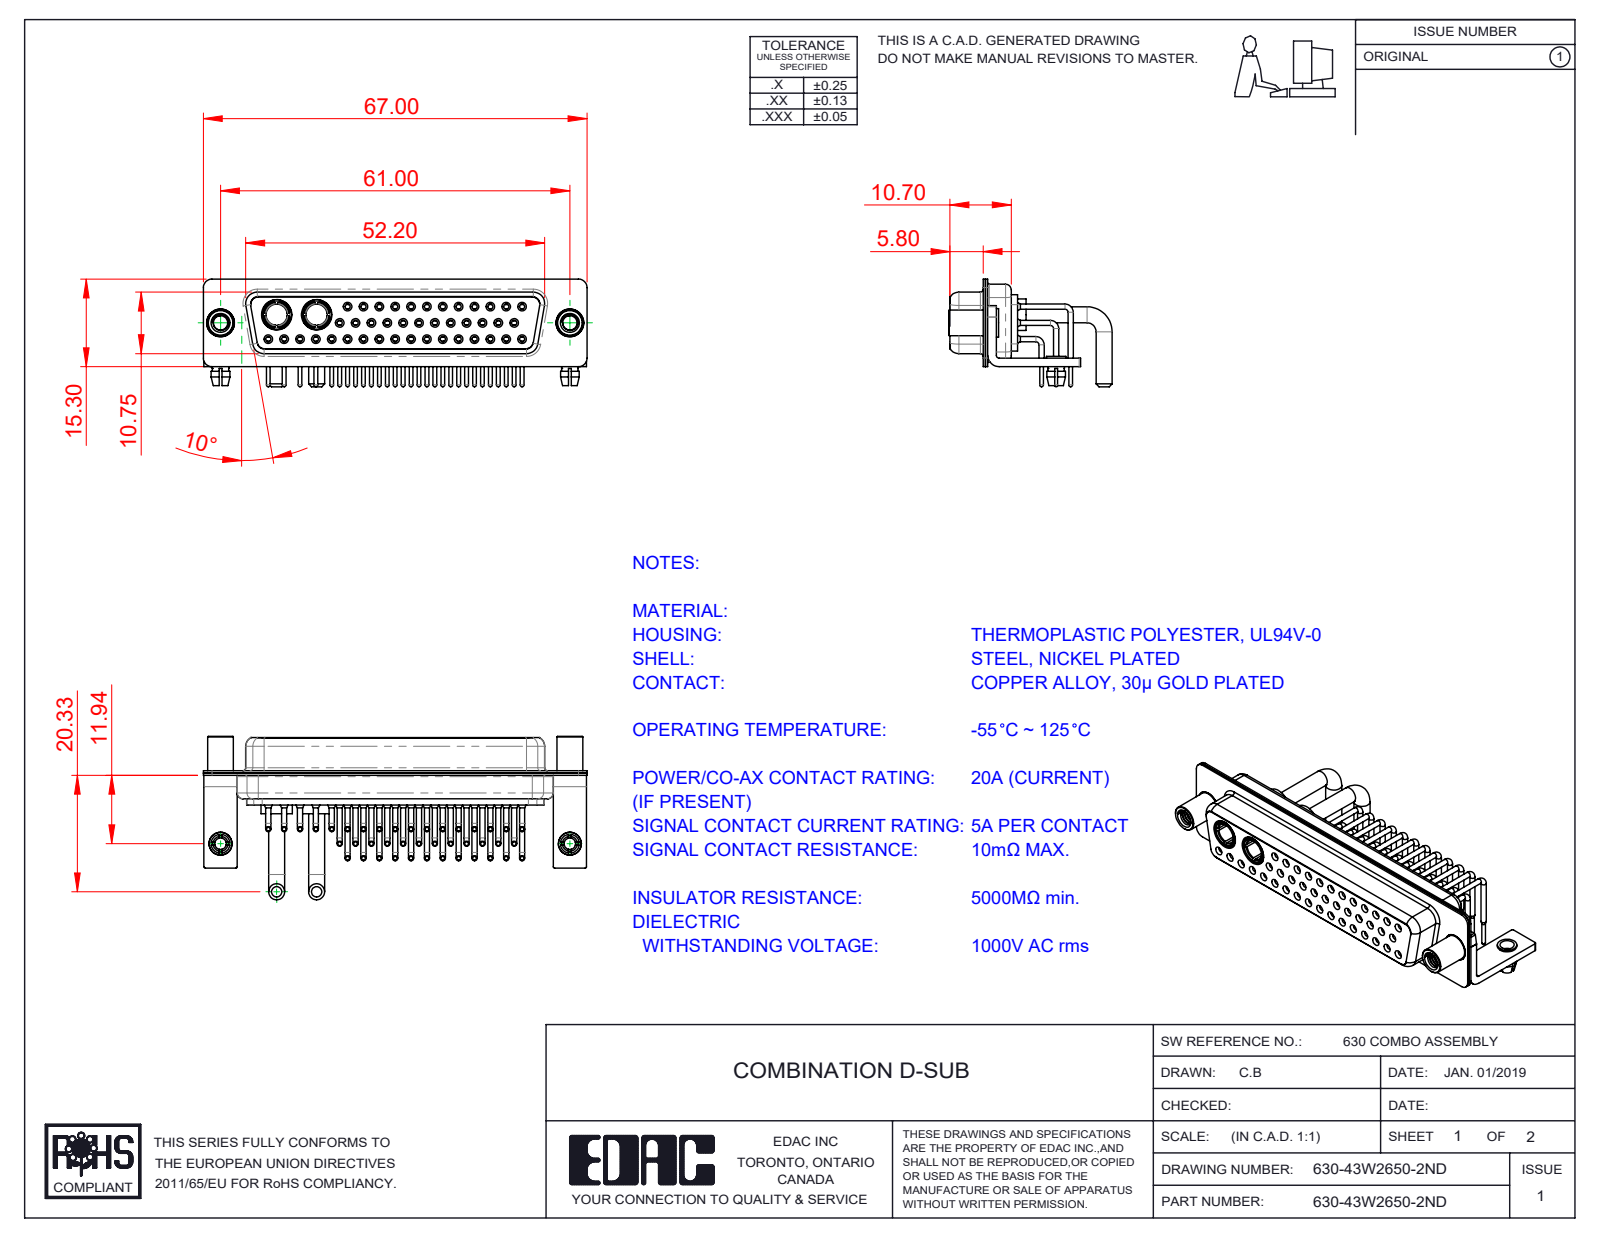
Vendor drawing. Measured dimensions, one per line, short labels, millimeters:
name: 630Combo Contact Row 2_50 Contacts; 630Combo Shell Front_50 Contacts; 630-43W2650-2ND; 630Combo Housing_43W2 (+7 more)
written by: SolidWorks 2020 (CONFIG_CONTROL_DESIGN)
unit: mm
bodies: 54 solids, 2798 faces (810 planar, 1234 cylindrical, 754 other)
size: 67 × 28.53 × 18.8
volume: 7 808 mm³; area: 17 238 mm²
holes: 43× ⌀2, 41× ⌀0.9, 41× ⌀1.1, 41× ⌀1.5, 29× ⌀1.6, 12× ⌀1.7, 4× ⌀2.5, 4× ⌀4.85, 2× ⌀3.2, 2× ⌀3.7, 2× ⌀4, 2× ⌀4.05
bosses: 41× ⌀0.9, 41× ⌀0.65, 12× ⌀1.6, 4× ⌀2.8, 2× ⌀5.5, 2× ⌀5.2, 2× ⌀5, 2× ⌀4.96
rounds: 16× R0.25, 16× R1.5, 13× R2, 12× R1.35, 8× R1.6, 5× R0.5, 4× R0.6, 4× R0.65
face distances: 0.4, 1.5, 6, 5.6, 0.8, 5.8, 5.2, 11.28, 1.82, 6.2
hole spacings: 2.77, 3.16, 5.54, 8.31, 11.08, 13.85, 16.62, 19.39
